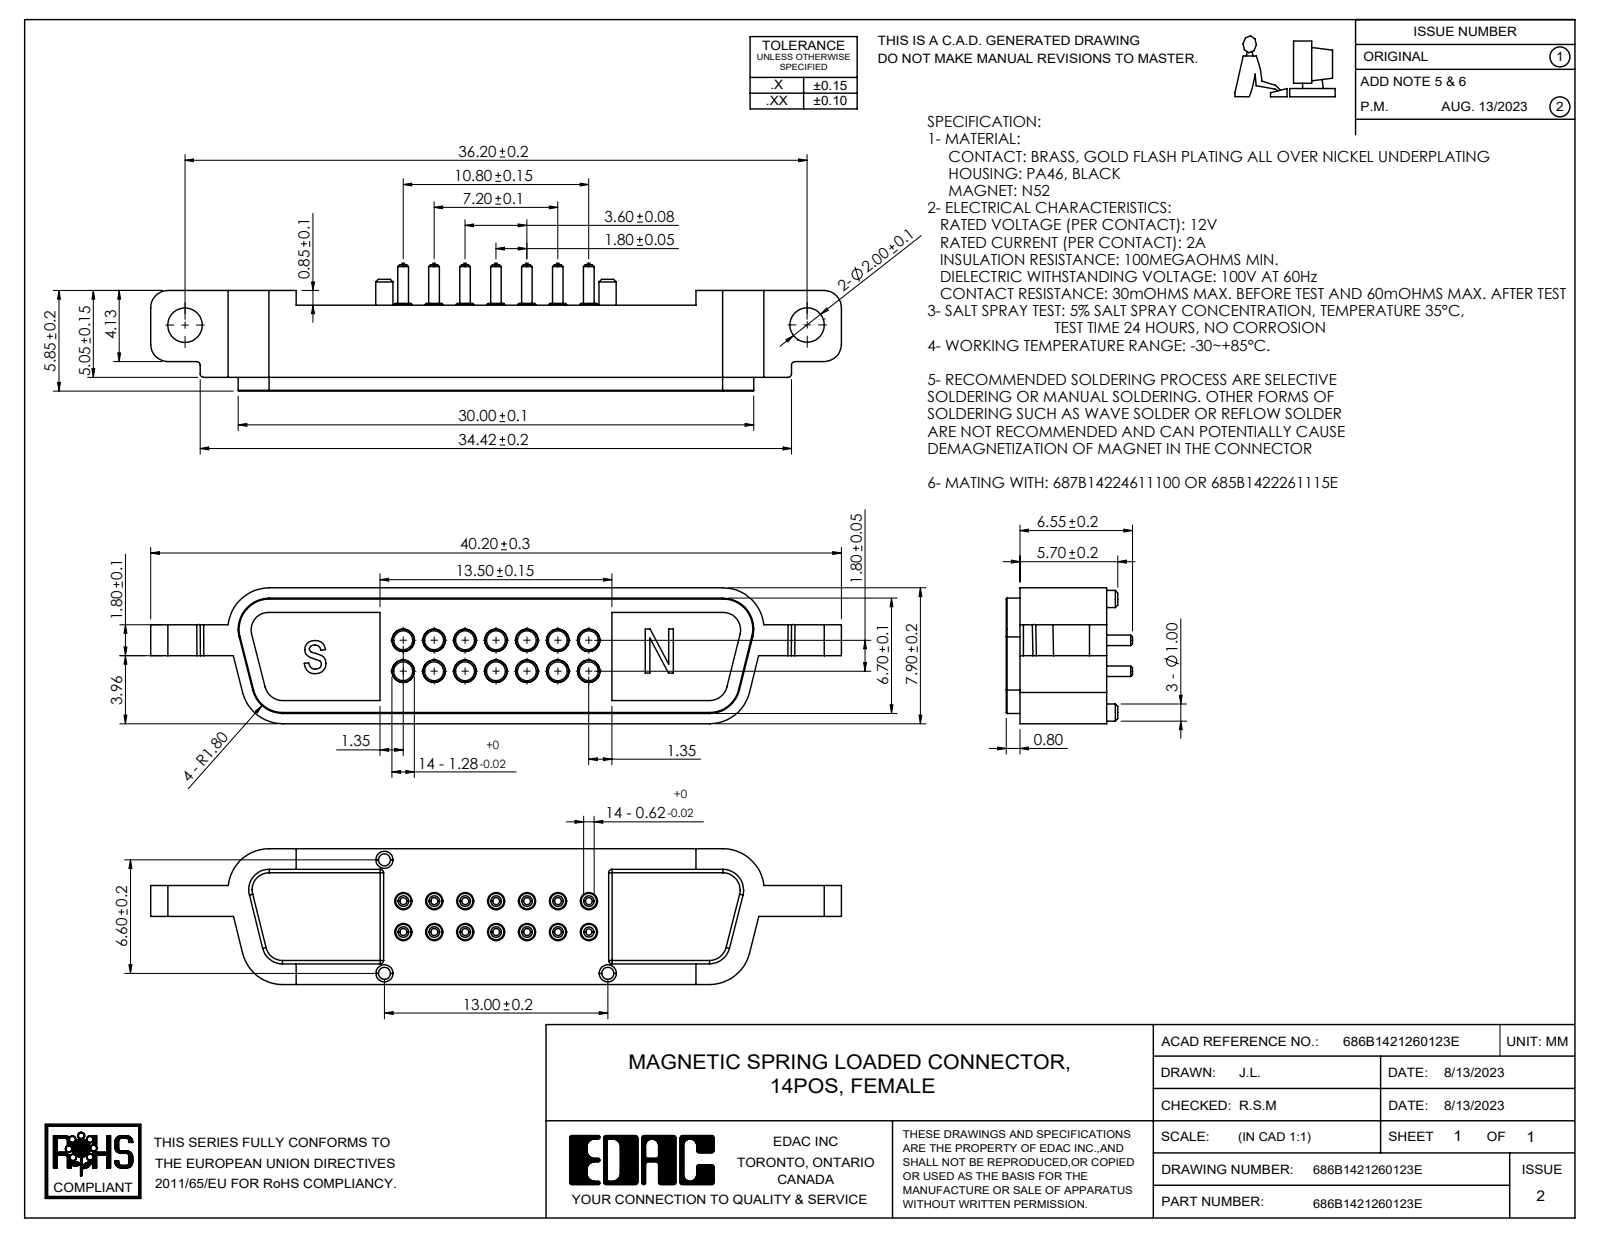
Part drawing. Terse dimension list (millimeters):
name: 686B1421260123E
written by: SolidWorks 2020 (CONFIG_CONTROL_DESIGN)
unit: mm
bodies: 1 solid, 431 faces (120 planar, 165 cylindrical, 146 other)
size: 40.2 × 7.9 × 7.35
volume: 1 236 mm³; area: 1 154 mm²
holes: 14× ⌀1.3, 1× ⌀2, 1× ⌀2.01
bosses: 17× ⌀1, 14× ⌀1.3, 13× ⌀0.59, 1× ⌀0.56
rounds: 14× R0.2, 6× R1, 1× R1.04, 1× R1.05, 1× R1.18, 1× R1.19, 1× R1.2, 1× R1.22
face distances: 7.91, 5, 4.95, 0.6, 0.75, 0.8, 4.2, 5.05, 0.85, 5.85
hole spacings: 1.8, 2.55, 3.6, 4.02, 5.4, 5.69, 7.2, 7.42
